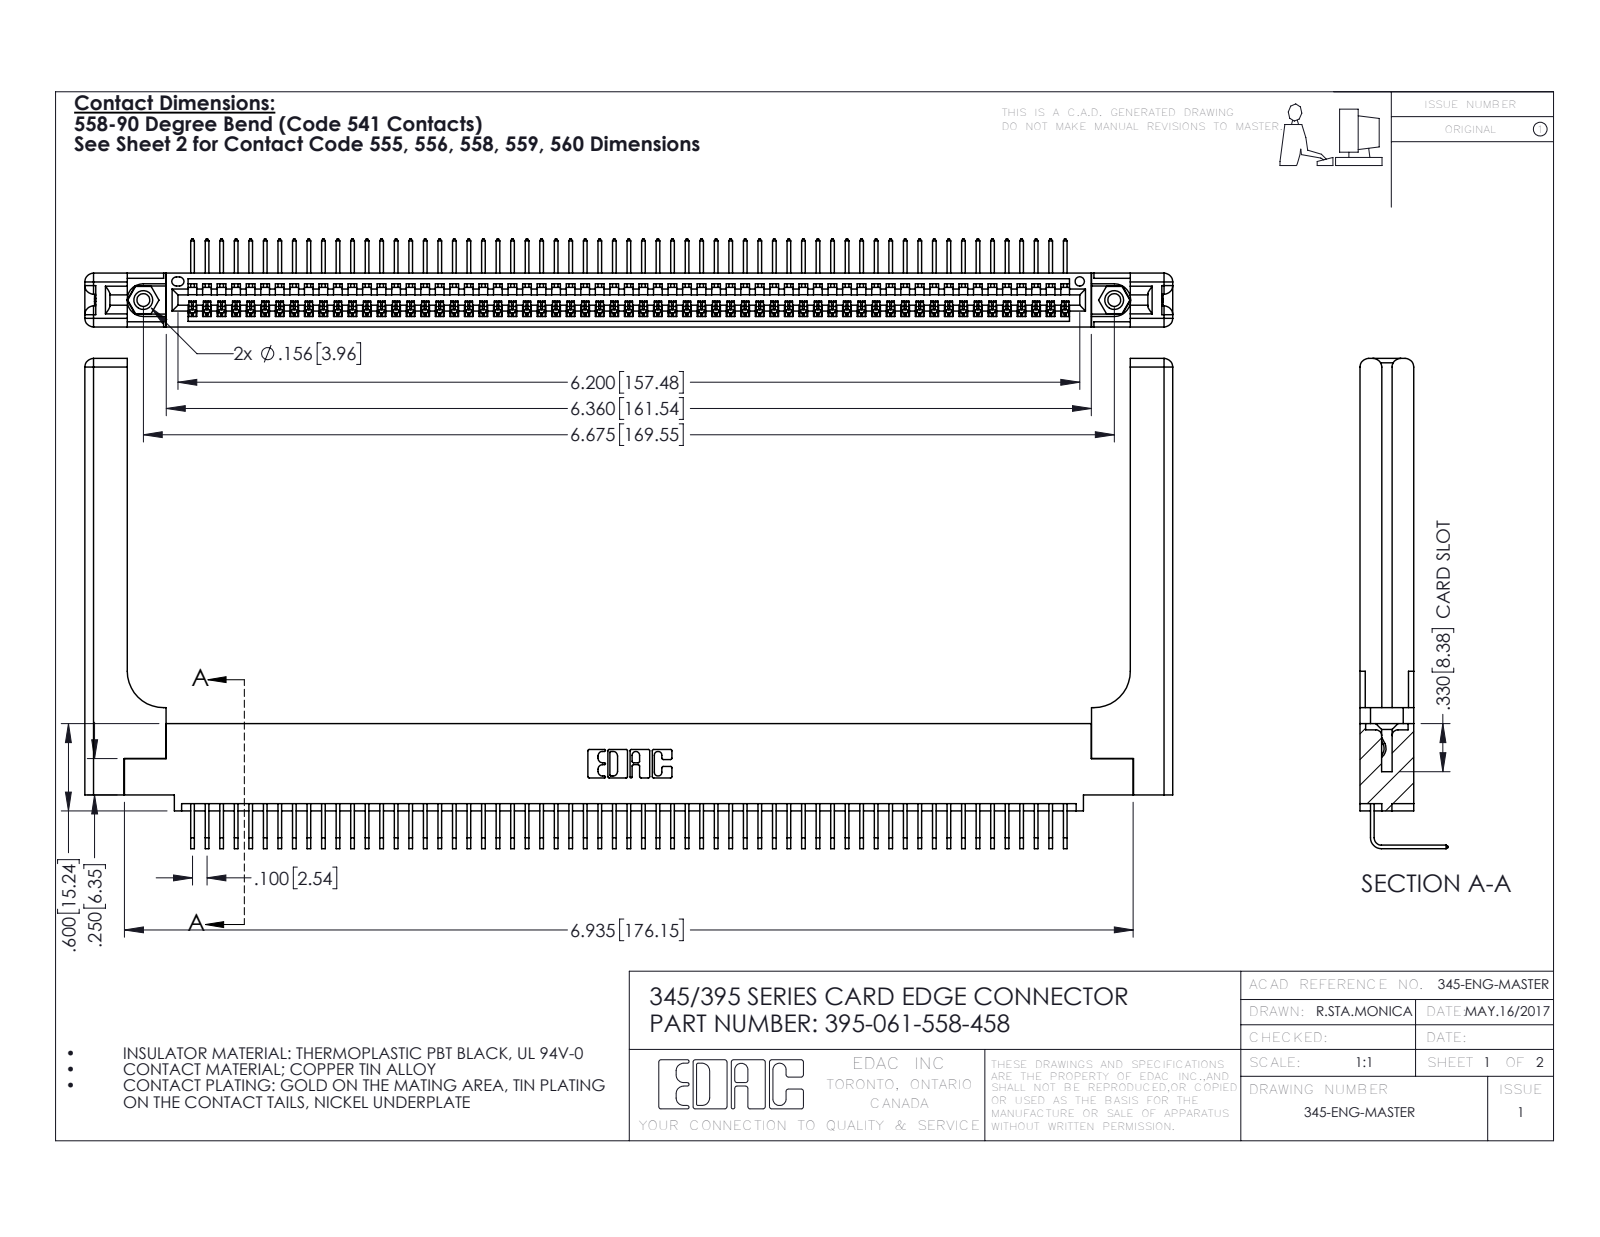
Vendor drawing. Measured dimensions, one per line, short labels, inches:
name: 395-061-558-458; 345-220-058_345-220-058; 345-250-001_345-250-001-102; 345-292-001_558 Tail - 2 (+1 more)
written by: SolidWorks 2016 (CONFIG_CONTROL_DESIGN)
unit: in
bodies: 66 solids, 4046 faces (2794 planar, 1192 cylindrical, 60 other)
size: 7.479 × 3.369 × 0.605
volume: 1.637 in³; area: 48.36 in²
holes: 2× ⌀0.089, 2× ⌀0.125, 2× ⌀0.156, 1× ⌀0.064
bosses: 2× ⌀0.155
rounds: 122× R0.006, 22× R0.01, 16× R0.06, 6× R0.007, 6× R0.031, 3× R0.026, 2× R0.03, 2× R0.031
face distances: 0.072, 0.37, 0.298, 0.098, 0.272, 0.025, 0.2, 0.225, 0.148, 0.15
hole spacings: 0.27, 6.439, 6.675
